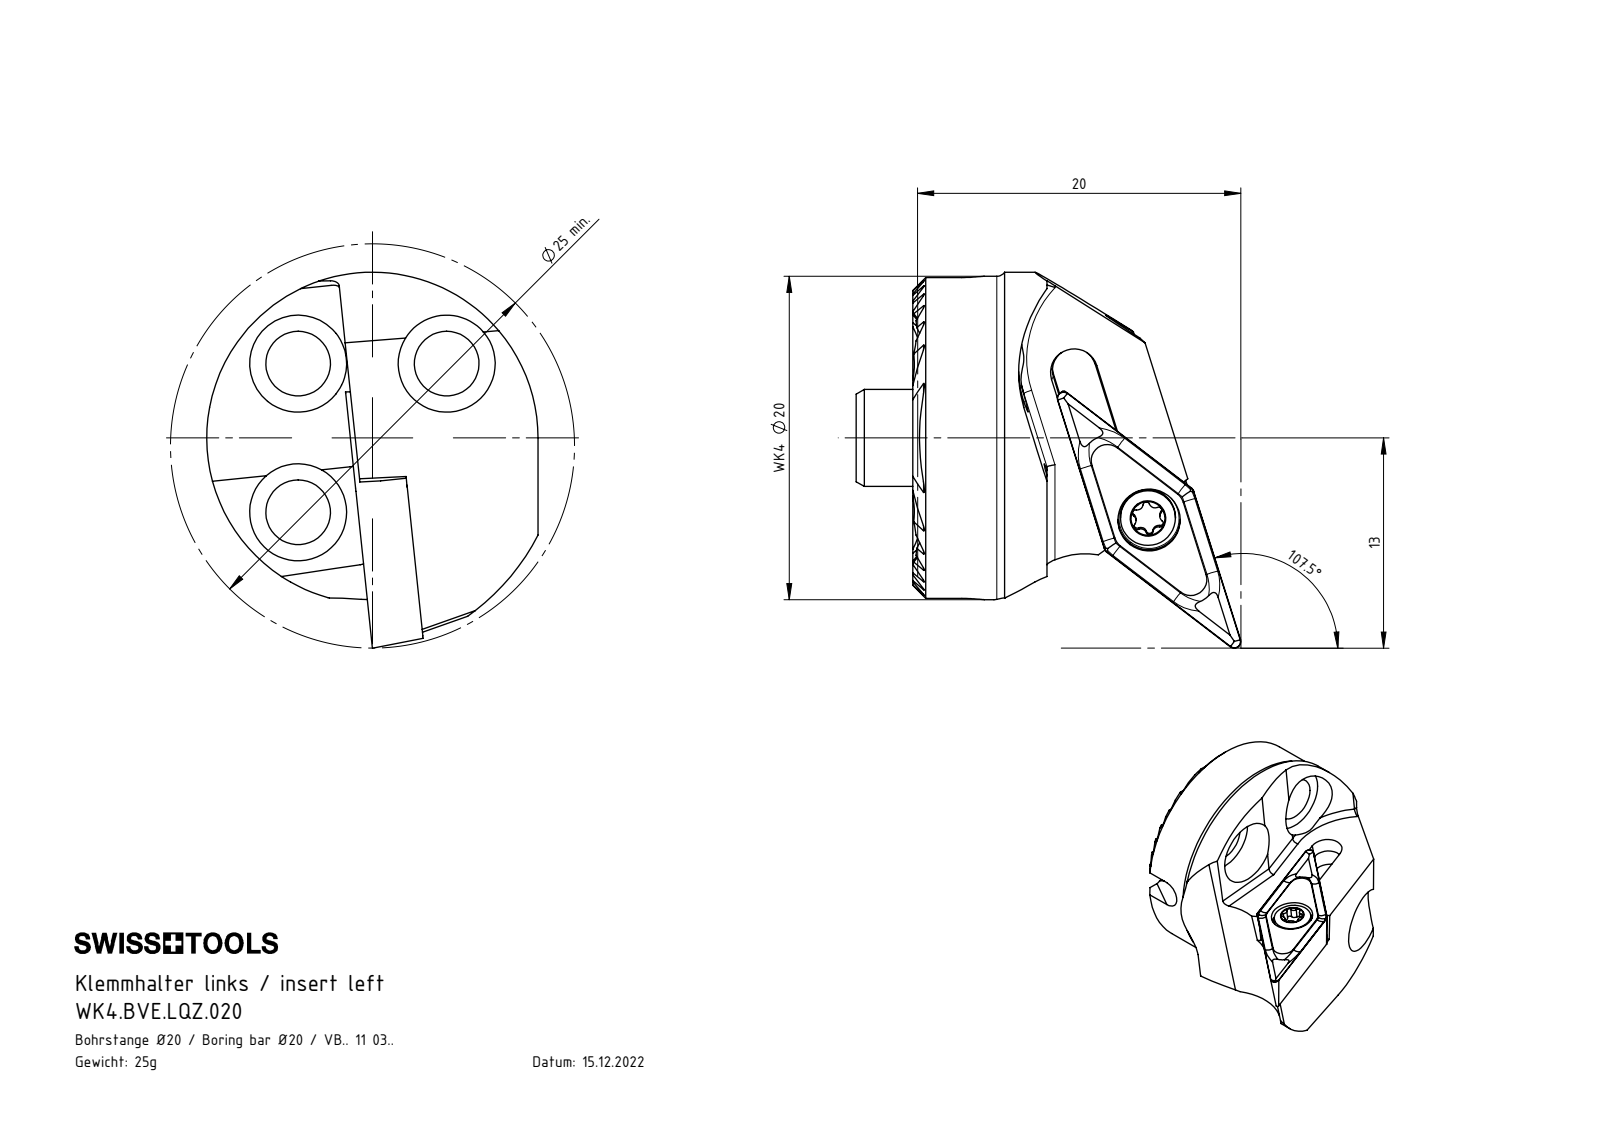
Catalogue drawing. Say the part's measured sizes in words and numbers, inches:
The part is named "VBMT110304; WCA-ER2.001.006_B; WK4.BVE.LQZ.020; WK3-ER1.001.006_A_Fertigbearbeitung (+1 more)". Its 3-D file was written by "SolidWorks 2017 (AUTOMOTIVE_DESIGN)". It is 4 solids with 338 faces: 142 planar, 123 cylindrical and 73 other. Overall it measures 0.937 by 0.915 by 0.807 inches. Its volume is 0.187 cubic inches and its surface area 4.219 square inches. Round holes: 3 of diameter 0.157, 3 of diameter 0.236, 1 of diameter 0.081, 1 of diameter 0.11, 1 of diameter 0.152, 1 of diameter 0.165, 1 of diameter 0.235. Round bosses or shafts: 1 of diameter 0.787, 1 of diameter 0.236, 1 of diameter 0.134, 1 of diameter 0.098. Partial cylindrical surfaces (rounded edges, fillets, slot ends): 16 of radius 0.005, 6 of radius 0.008, 5 of radius 0.014, 2 of radius 0.02, 2 of radius 0.197, 1 of radius 0.014, 1 of radius 0.053, 1 of radius 0.276. The main face-to-face distances are 0.17, 0.043, 0.128, 0.085, 0.213, 0.341, 0.085, 0.113, 0.298, 0.256. The hole center spacings are 0.256, 0.362, 0.512.
